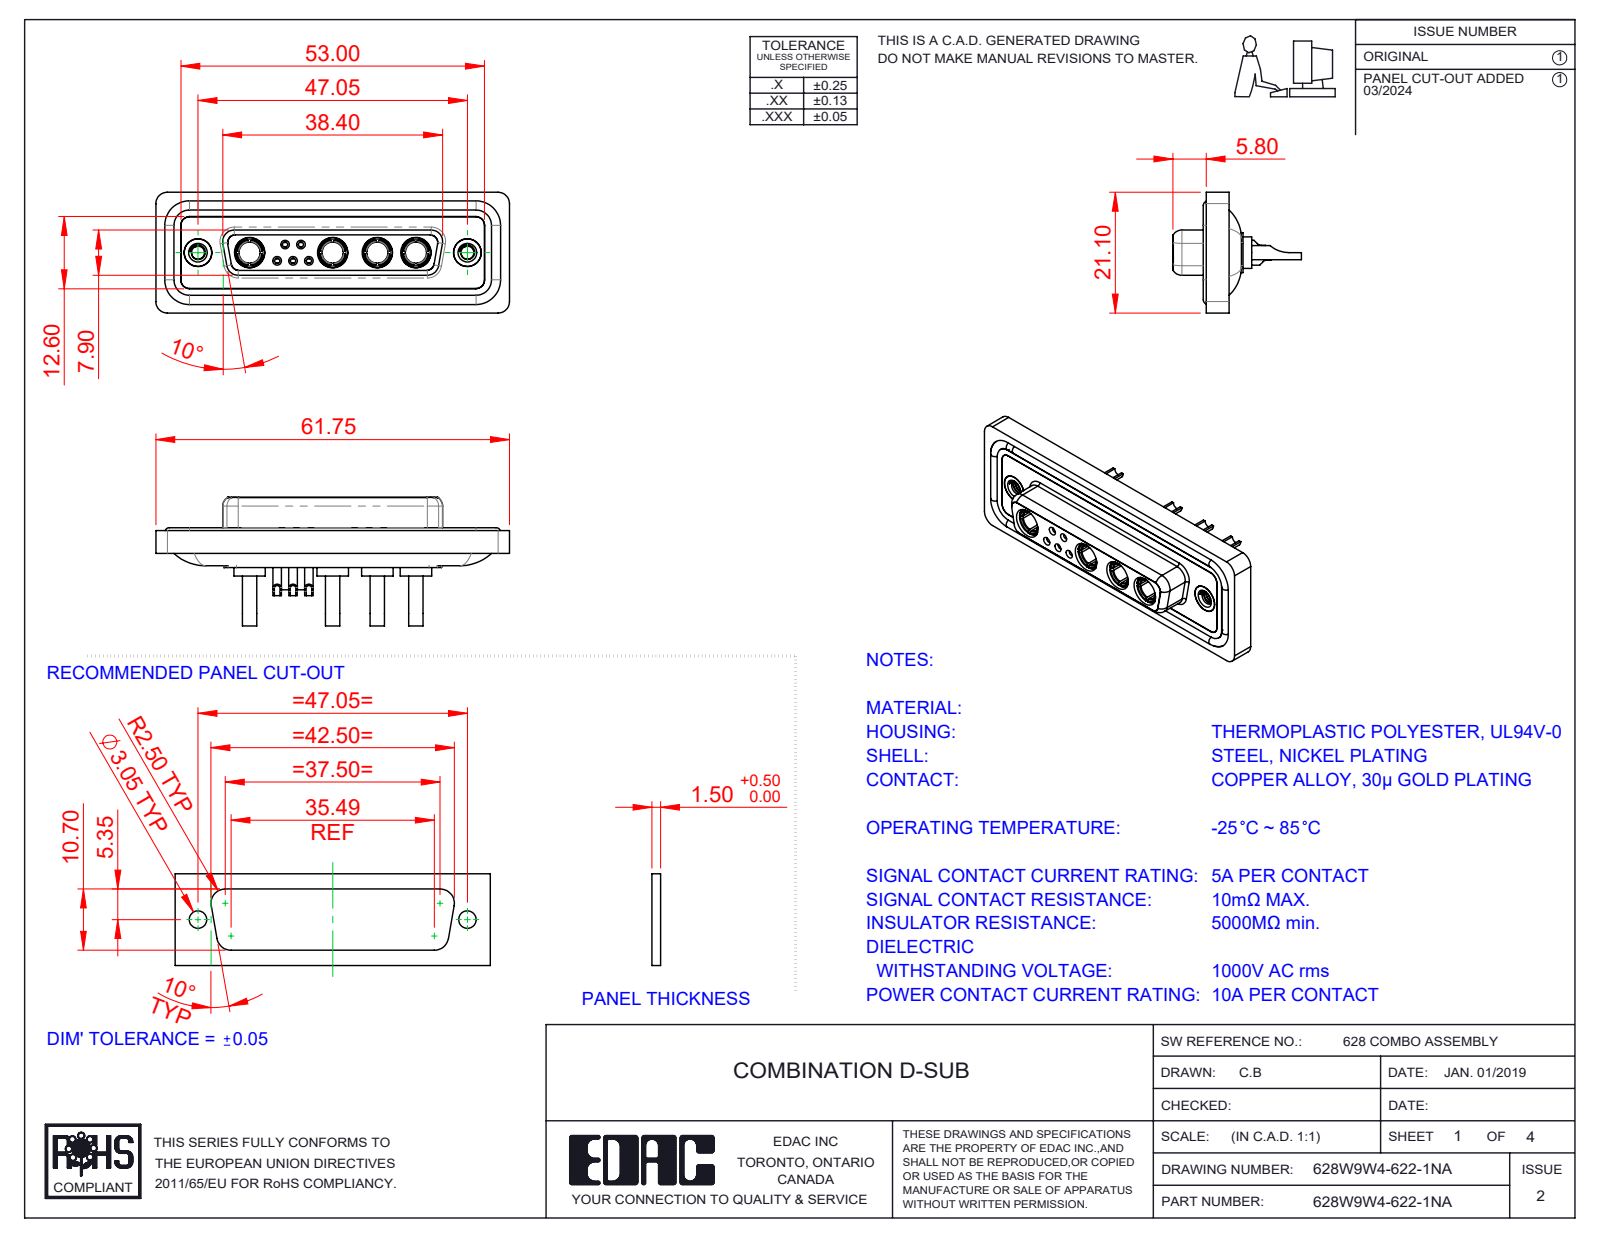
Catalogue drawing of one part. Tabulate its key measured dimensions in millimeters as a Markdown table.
| quantity | value |
| --- | --- |
| part name | 628Combo Shell Front_25 Contacts; 628Combo Contact Row 1_22; 628W9W4-622-1NA; 628Combo Threaded Rivet_A (+5 more) |
| STEP written by | SolidWorks 2023 (CONFIG_CONTROL_DESIGN) |
| units | millimeters |
| bodies | 20 solids, 975 faces (314 planar, 399 cylindrical, 262 other) |
| overall size | 61.75 × 22.45 × 21.1 |
| volume | 8 225 mm³ |
| surface area | 13 805 mm² |
| round holes (diameter × count) | 4.85 × 6, 0.9 × 5, 1 × 5, 1.1 × 5, 1.5 × 5, 2 × 5, 1.7 × 4, 3.7 × 4, 5.3 × 4, 1.6 × 3, 1.7 × 2, 2.26 × 2 |
| round bosses / shafts (diameter × count) | 1.6 × 6, 2.2 × 5, 5.5 × 4, 5.2 × 4, 4.96 × 4, 4.75 × 4, 3.75 × 4, 2.5 × 4 |
| partial cylindrical surfaces (radius × count) | 1.5 × 22, 2 × 18, 1.35 × 8, 1.6 × 8, 1 × 6, 0.25 × 4, 0.5 × 4, 0.6 × 4 |
| main face-to-face distances | 0.4, 1.8, 7.45, 5.65, 0.5, 7.05, 6.6, 1.6, 1.1, 2.9 |
| hole center spacings | 3.16, 2.77, 5.03, 2.76, 4.4, 5.02, 5.54, 5.73 |
